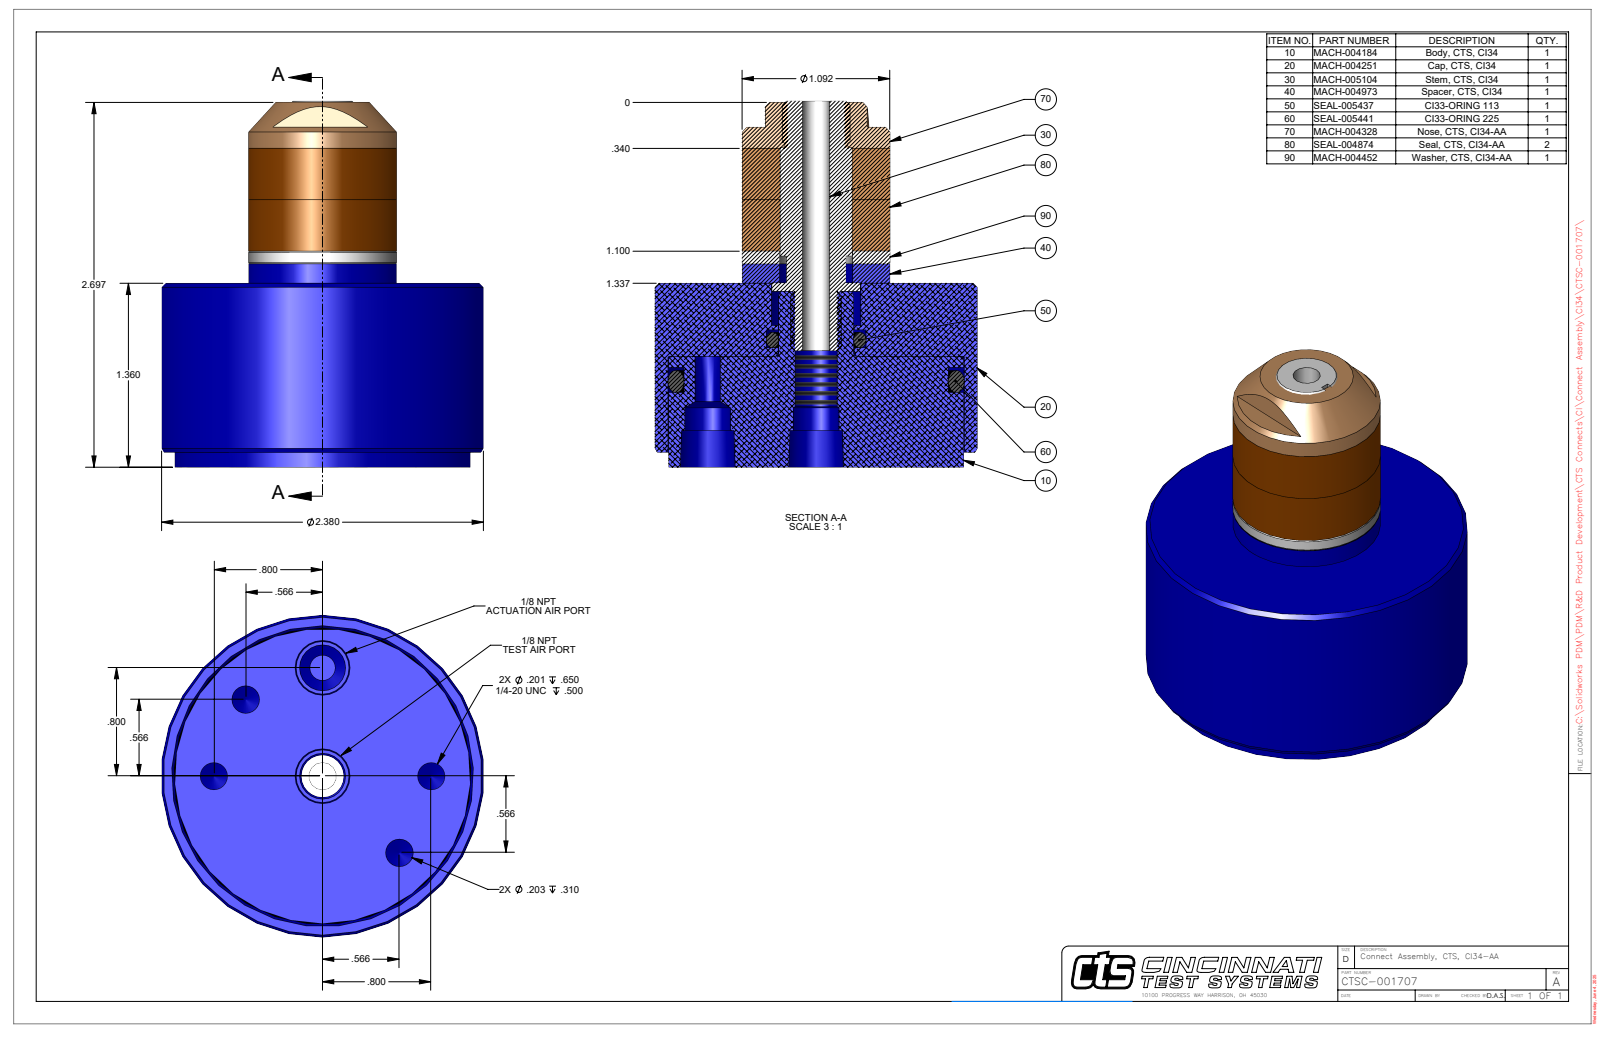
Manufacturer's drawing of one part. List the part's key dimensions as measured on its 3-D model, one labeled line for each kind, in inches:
Part name (STEP PRODUCT): CTSC-001707
STEP written by: SolidWorks 2023 (AUTOMOTIVE_DESIGN)
Units: inches
Bodies: 1 solid, 76 faces (22 planar, 27 cylindrical, 27 other)
Overall size (bounding box): 2.706 × 2.38 × 2.38
Volume: 6.909 in³ · Surface area: 30.98 in²
Round holes (diameter × count): ⌀0.201 ×2, ⌀0.203 ×2, ⌀0.339 ×2, ⌀0.203 ×1, ⌀2.188 ×1
Round bosses / shafts (diameter × count): ⌀2.38 ×1, ⌀2.178 ×1, ⌀1.092 ×1, ⌀1.09 ×1
Partial cylindrical surfaces — rounded edges, fillets, slot ends (radius × count): R0.211 ×1
Main face-to-face distances: 1.36, 0.11, 1.25, 0.448, 0.338, 0.912, 2.697, 2.587, 2.249, 1.337
Hole centre spacings: 0.8, 0.612, 1.478, 1.131, 1.6
